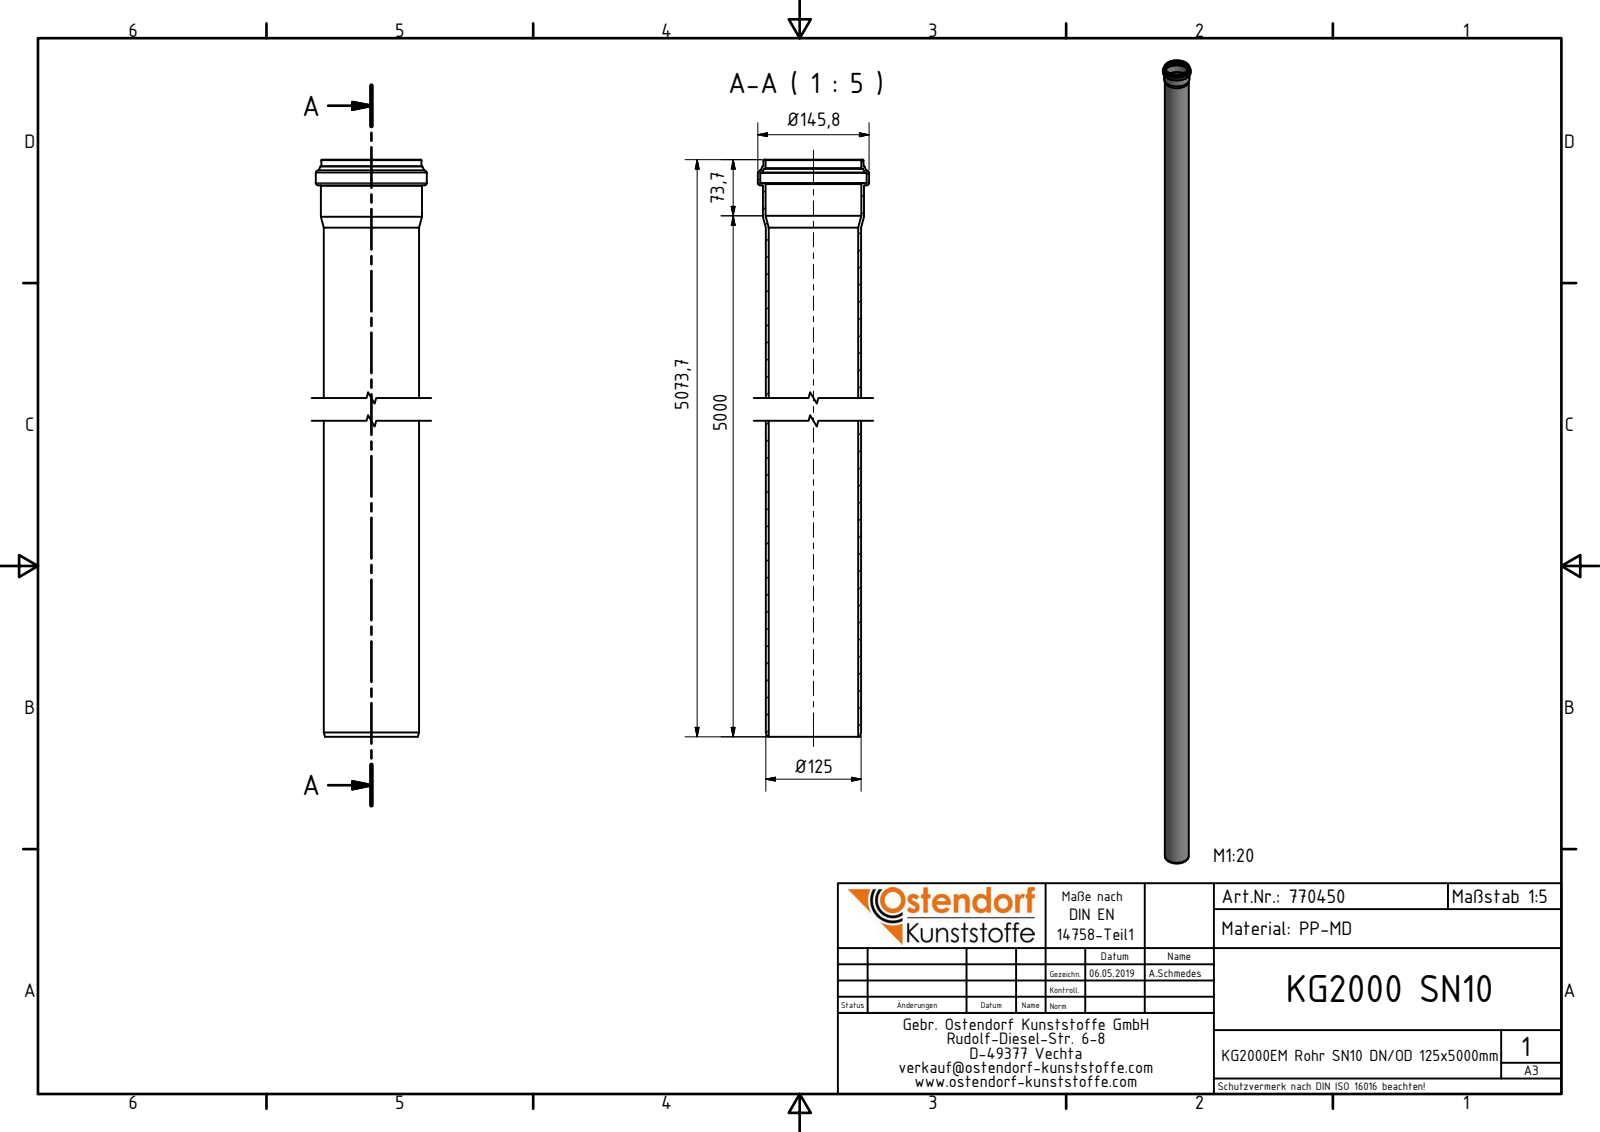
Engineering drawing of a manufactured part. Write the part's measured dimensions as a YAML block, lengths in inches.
part_name: "770480 KG2000EM Rohr SN10 DN-OD125x5000"
step_written_by: "Autodesk Inventor 2016 (AUTOMOTIVE_DESIGN)"
units: inches
bodies: {solids: 1, faces: 35, planar: 5, cylindrical: 8, other: 22}
overall_size: [199.752, 5.74, 5.74]
volume: 459.6
surface_area: 6008
round_holes:
  - {diameter: 4.614, count: 1}
  - {diameter: 4.941, count: 1}
  - {diameter: 5.504, count: 1}
round_bosses_or_shafts:
  - {diameter: 5.74, count: 1}
  - {diameter: 5.224, count: 1}
  - {diameter: 5.177, count: 1}
  - {diameter: 4.921, count: 1}
face_to_face_distances: [198.425, 199.752, 1.327, 199.404, 0.979, 0.348, 199.193, 0.768, 0.211, 0.559]
